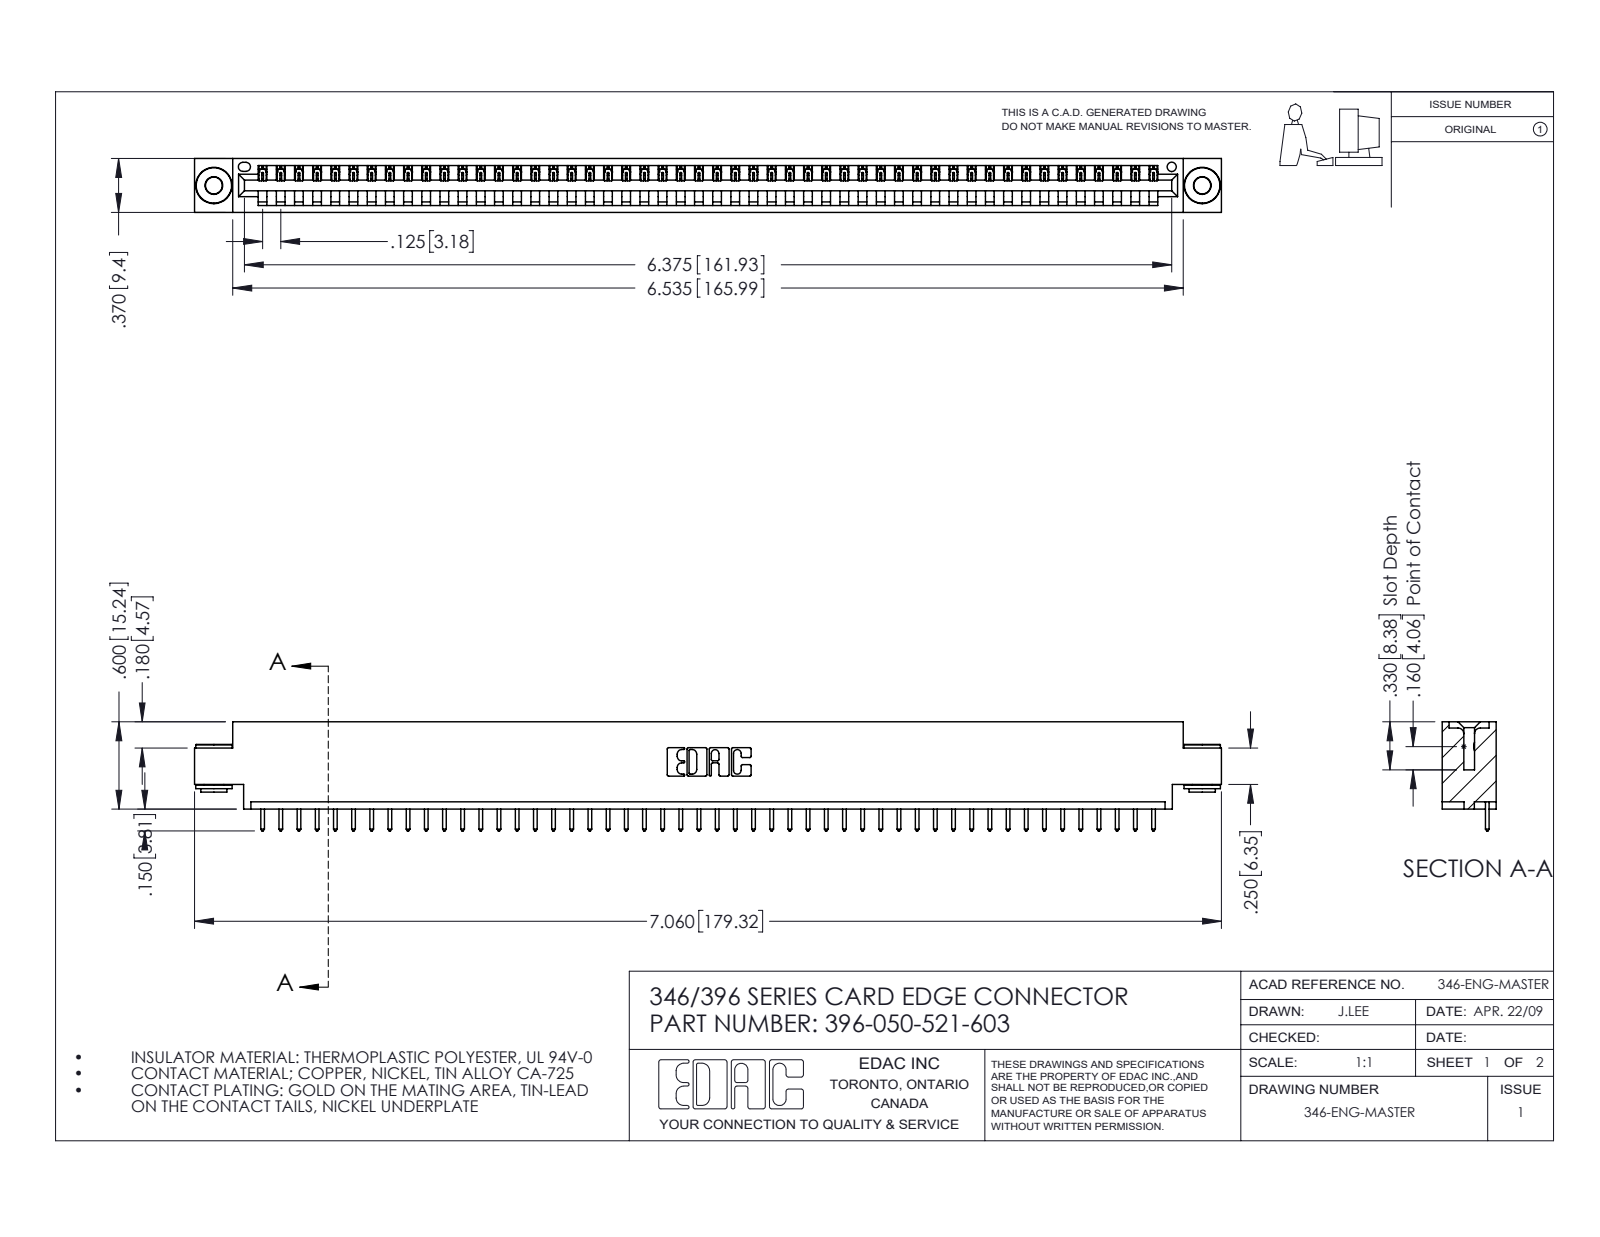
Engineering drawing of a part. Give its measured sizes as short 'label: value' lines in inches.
name: 345-250-002_345-250-002-102; 396-050-521-603; 345-292-001_345-293-121; 346 Part_0.170 Offset - 0.156 Dia-TH
written by: SolidWorks 2016 (CONFIG_CONTROL_DESIGN)
unit: in
bodies: 53 solids, 3064 faces (2090 planar, 966 cylindrical, 8 other)
size: 7.06 × 0.75 × 0.37
volume: 1.034 in³; area: 32.67 in²
holes: 2× ⌀0.116, 2× ⌀0.156, 1× ⌀0.064
bosses: 2× ⌀0.25, 2× ⌀0.18, 2× ⌀0.136
rounds: 100× R0.006, 100× R0.01, 22× R0.01, 6× R0.007, 6× R0.031, 3× R0.026, 2× R0.031, 2× R0.04
face distances: 0.048, 0.322, 0.37, 0.25, 0.025, 0.072, 0.298, 0.148, 0.222, 0.1
hole spacings: 0.246, 6.586, 6.795
